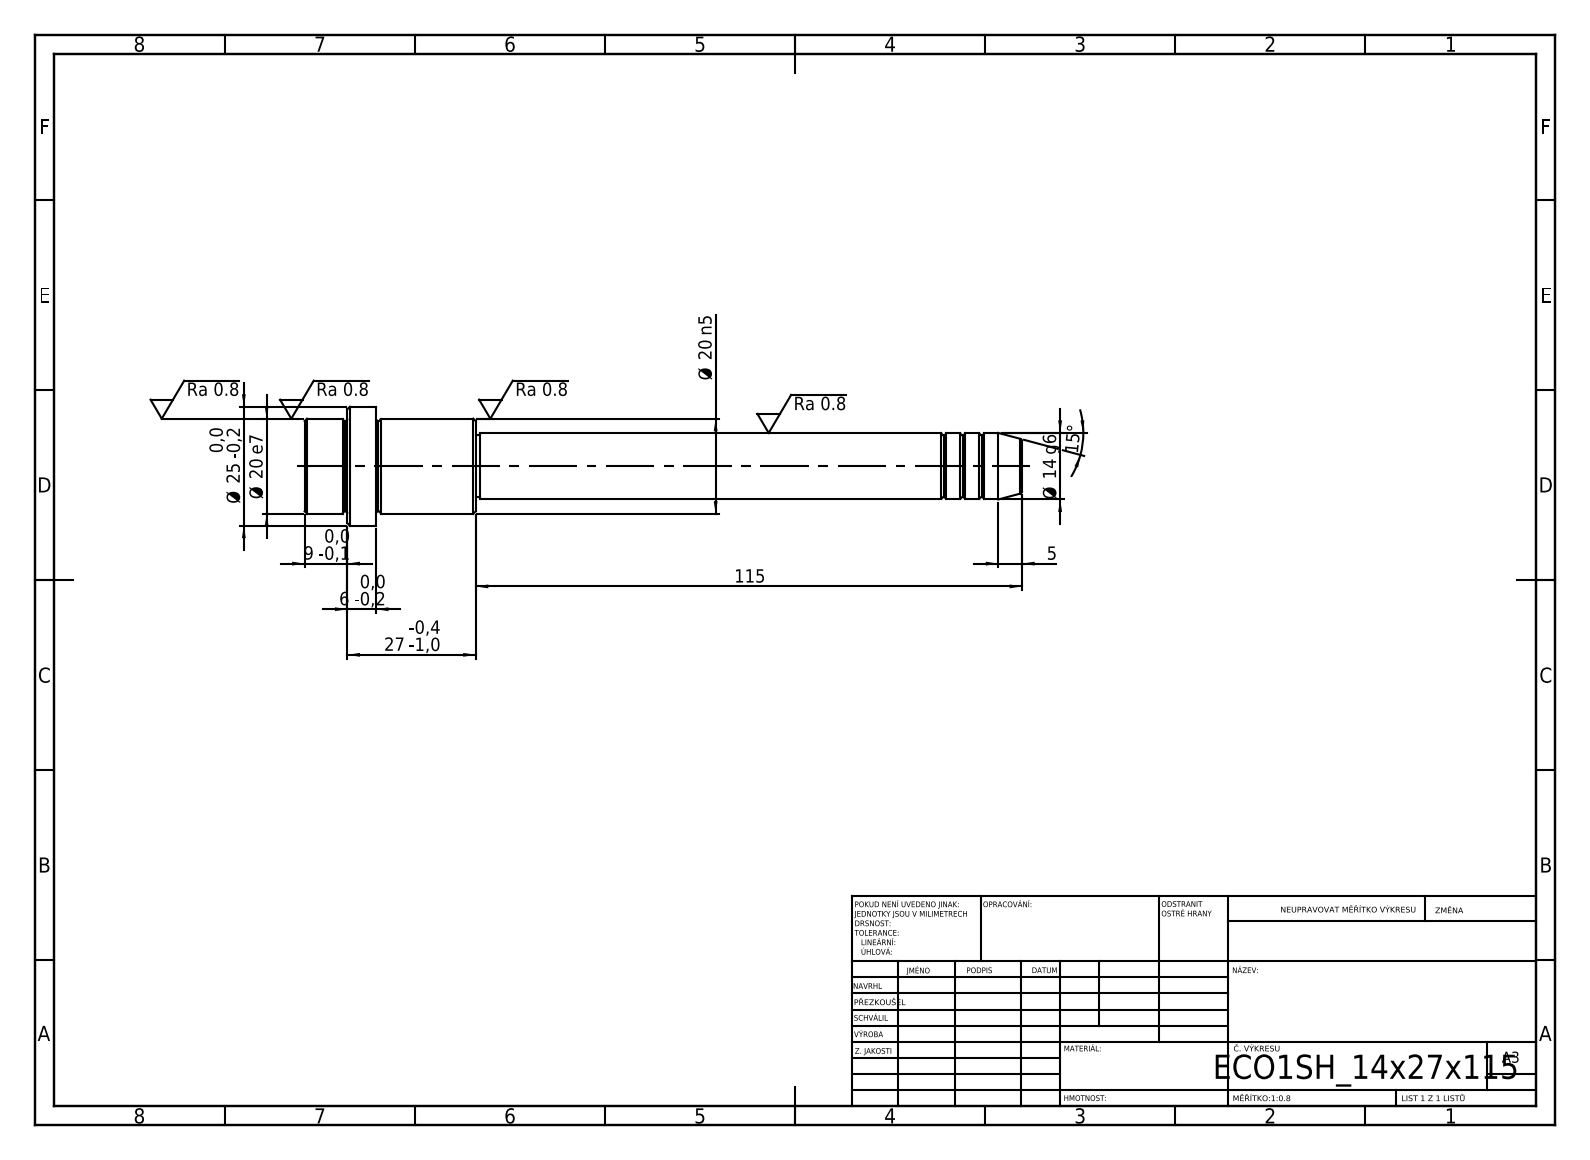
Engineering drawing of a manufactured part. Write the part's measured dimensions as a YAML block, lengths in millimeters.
step_written_by: "SolidWorks 2019 (CONFIG_CONTROL_DESIGN)"
units: millimeters
bodies: {solids: 1, faces: 52, planar: 6, cylindrical: 16, other: 30}
overall_size: [151, 25, 25]
volume: 29789
surface_area: 8434
round_bosses_or_shafts:
  - {diameter: 25, count: 1}
  - {diameter: 20, count: 1}
  - {diameter: 14, count: 1}
  - {diameter: 13, count: 1}
face_to_face_distances: [15, 21, 36, 27, 6, 9, 115, 136, 142, 151]
